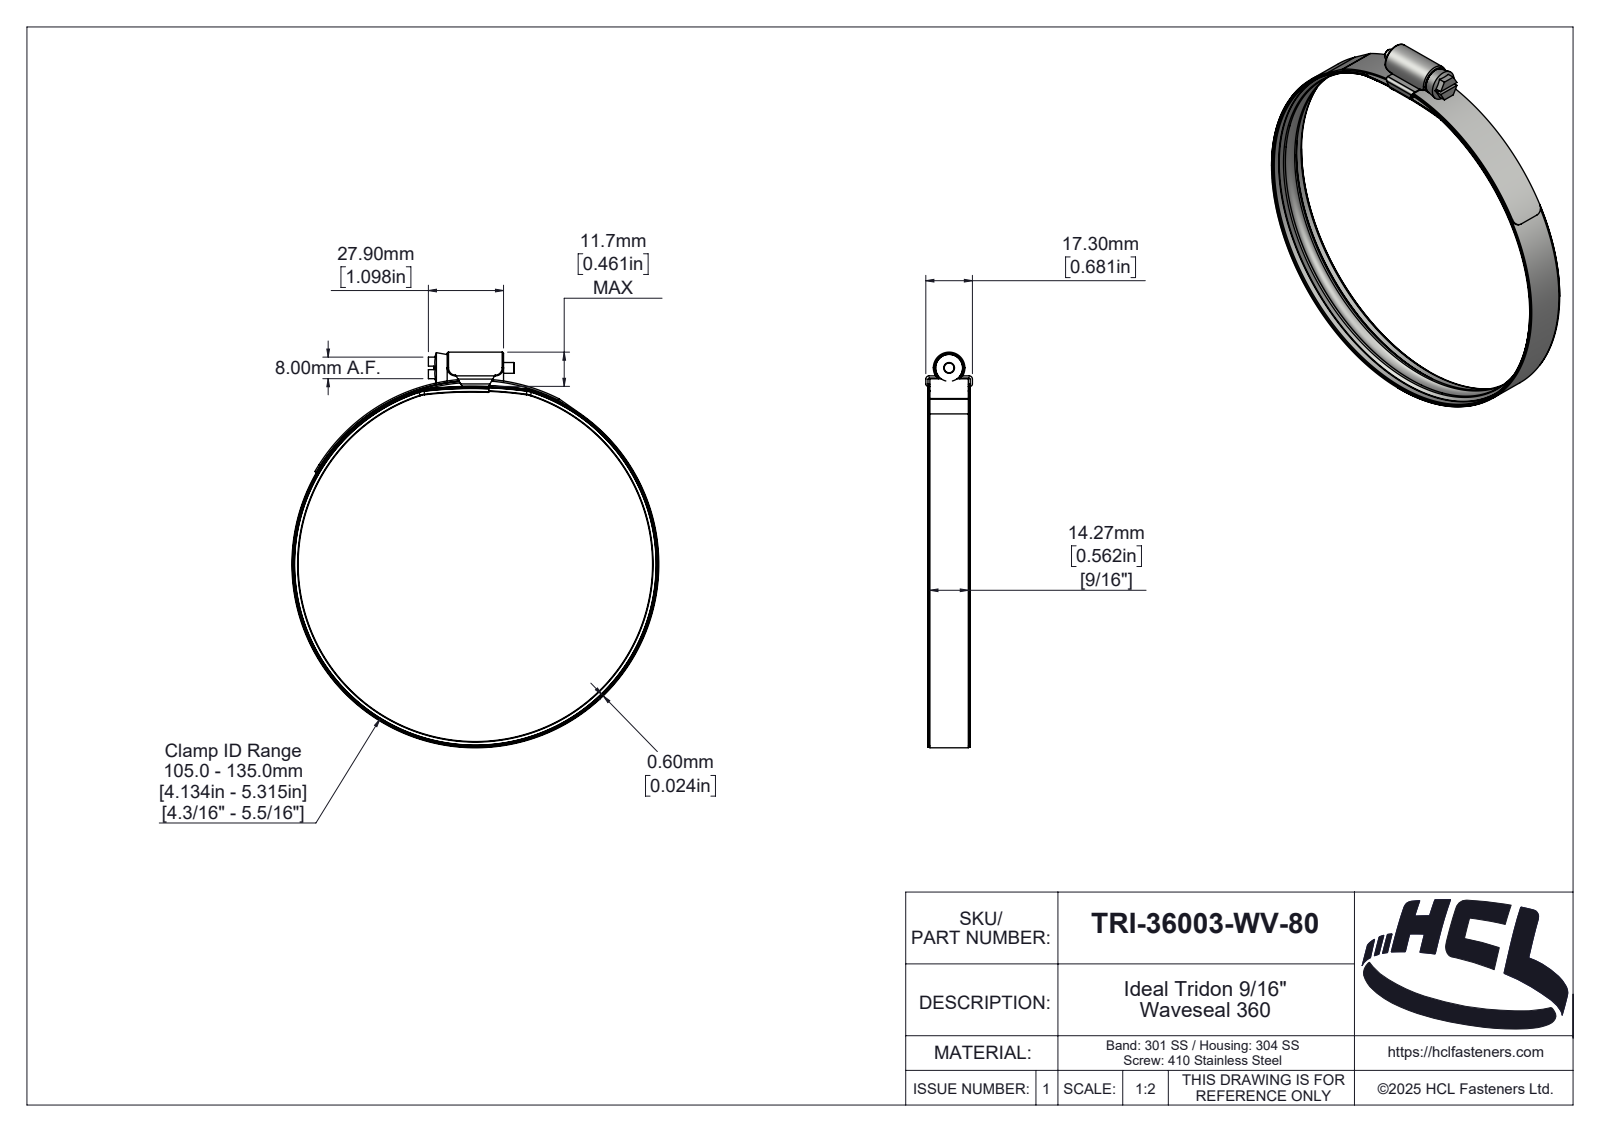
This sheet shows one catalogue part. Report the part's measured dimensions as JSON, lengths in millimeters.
{"part_name": "TRI-36003-WV-80", "step_written_by": "SolidWorks 2025 (AUTOMOTIVE_DESIGN)", "units": "millimeters", "bodies": {"solids": 4, "faces": 418, "planar": 42, "cylindrical": 119, "other": 257}, "overall_size": [146.8, 136.2, 17.3], "volume_mm3": 8627, "surface_area_mm2": 32936, "round_holes": [[134.4, 1], [135, 1]], "round_bosses_or_shafts": [[136.2, 1], [134.8, 1], [10, 1], [4, 1]], "partial_cylinders_radius": [[0.5, 6], [3, 4], [0.1, 2], [0.9, 2], [1.2, 2], [9.9, 2], [10.1, 2], [0.46, 1]], "face_to_face_distances": [14.26, 0.8, 3.1, 0.6, 2.3, 3.9, 27.9, 1.52, 15.78, 16.5]}
